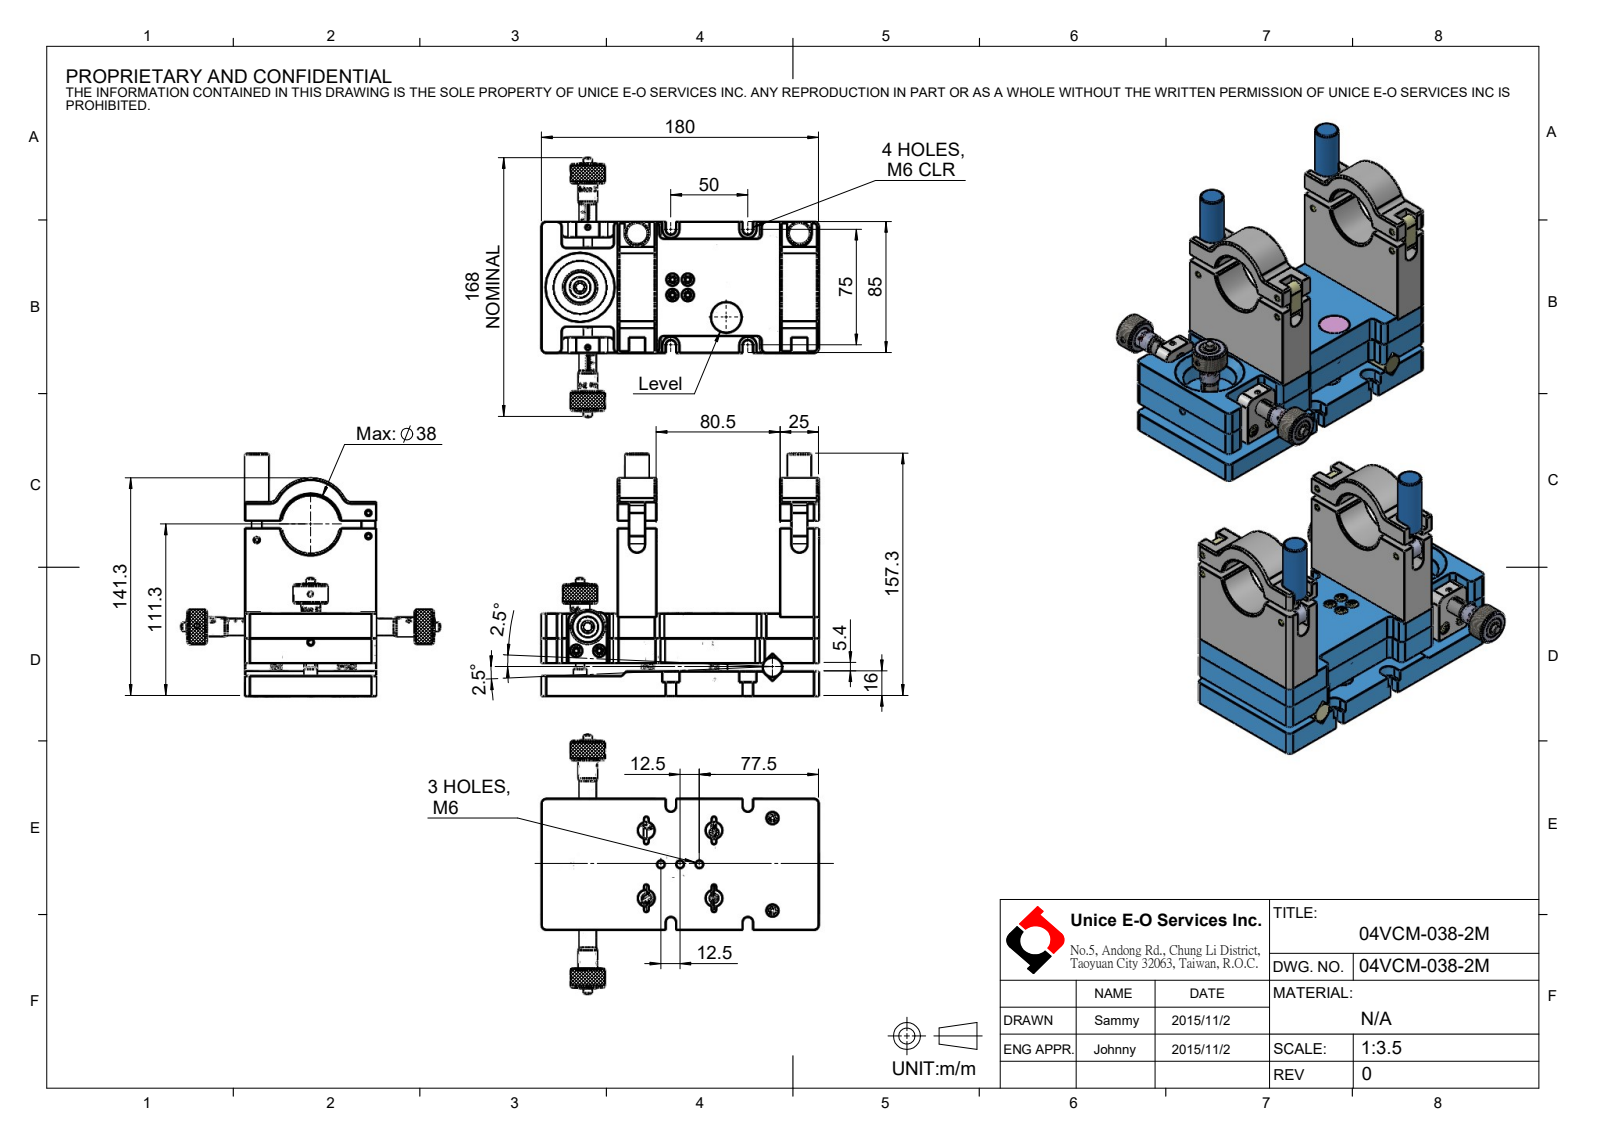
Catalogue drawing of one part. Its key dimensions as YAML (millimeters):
part_name: "04VCM-038-2M"
step_written_by: "SolidWorks 2021 (CONFIG_CONTROL_DESIGN)"
units: millimeters
bodies: {solids: 0, faces: 756, planar: 337, cylindrical: 282, other: 137}
overall_size: [180, 168, 157.78]
round_holes:
  - {diameter: 8, count: 8}
  - {diameter: 3.3, count: 5}
  - {diameter: 1.2, count: 4}
  - {diameter: 11, count: 4}
  - {diameter: 4, count: 3}
  - {diameter: 5, count: 3}
  - {diameter: 13.3, count: 2}
  - {diameter: 4.3, count: 1}
  - {diameter: 35, count: 1}
  - {diameter: 38.2, count: 1}
round_bosses_or_shafts:
  - {diameter: 1.6, count: 4}
  - {diameter: 13, count: 3}
  - {diameter: 22, count: 2}
  - {diameter: 15, count: 2}
  - {diameter: 12, count: 2}
  - {diameter: 10.5, count: 2}
  - {diameter: 7, count: 2}
  - {diameter: 6, count: 2}
partial_cylinders:
  - {radius: 3, count: 32}
  - {radius: 1.5, count: 8}
  - {radius: 1, count: 6}
  - {radius: 5, count: 6}
  - {radius: 3.4, count: 4}
  - {radius: 5.6, count: 4}
  - {radius: 0.5, count: 2}
  - {radius: 4.5, count: 2}
face_to_face_distances: [16, 21.4, 37.5, 16.1, 37.4, 105.5, 25, 5.4, 21.5, 85]
hole_center_spacings: [31.91, 44, 7.07, 9.01, 10, 18.2, 23.96, 24.04]
